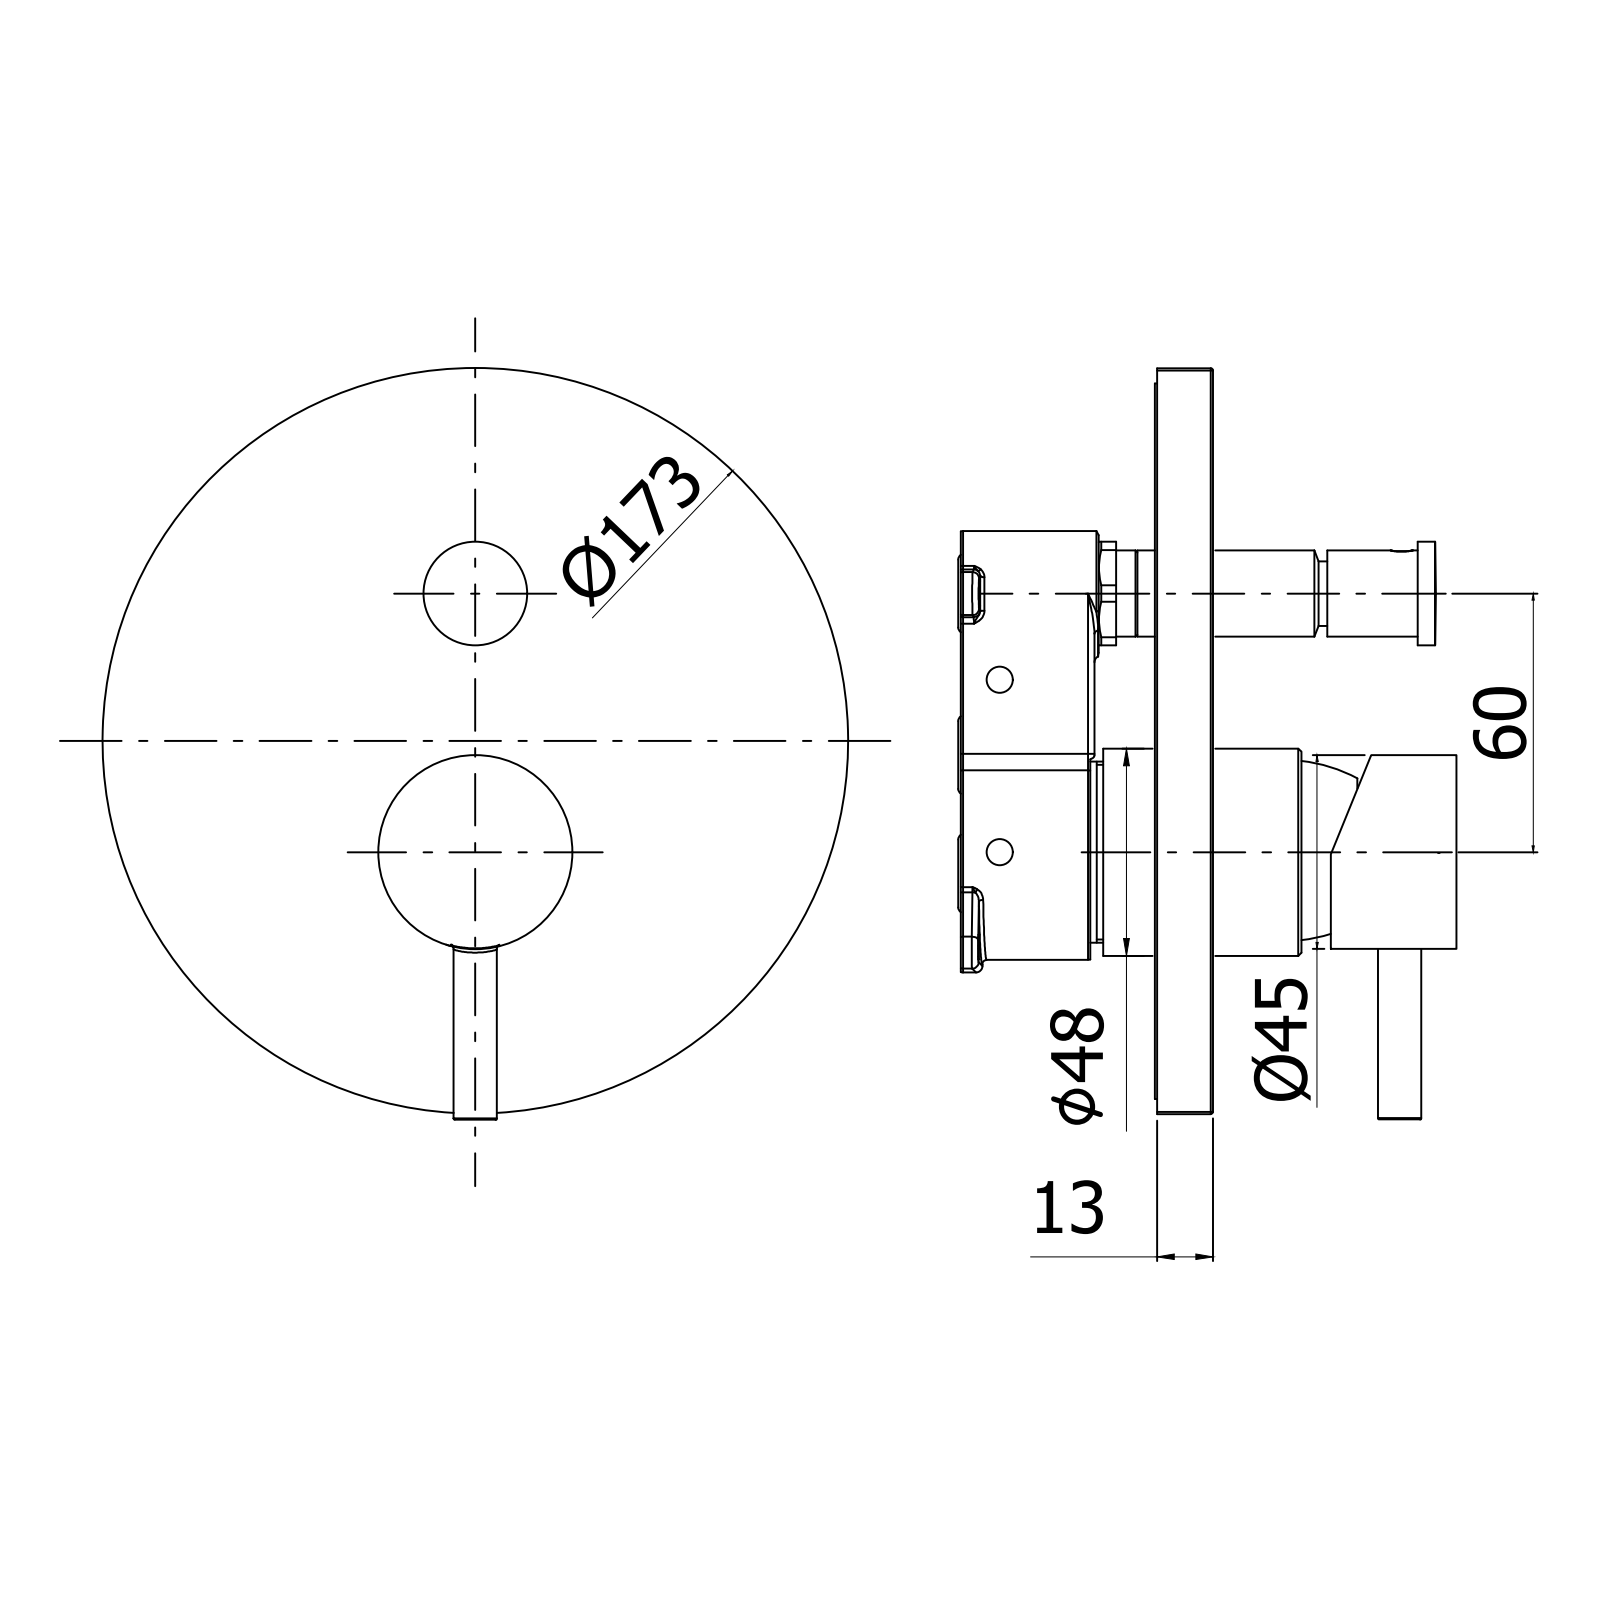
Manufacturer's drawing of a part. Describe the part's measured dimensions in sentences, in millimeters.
The part is named "LIGBOX015CR". Its 3-D file was written by "CREO PARAMETRIC BY PTC INC, 2020044 (CONFIG_CONTROL_DESIGN)". It is 1 solid with 169 faces: 34 planar, 48 cylindrical and 87 other. Overall it measures 174.25 by 173 by 58.69 millimeters. Its volume is 375 572 cubic millimeters and its surface area 71 572 square millimeters. Round holes: 1 of diameter 3, 1 of diameter 5.5. Round bosses or shafts: 1 of diameter 173, 1 of diameter 48.1, 1 of diameter 44.5, 1 of diameter 24, 1 of diameter 20, 1 of diameter 15, 1 of diameter 10, 1 of diameter 7.6. Partial cylindrical surfaces (rounded edges, fillets, slot ends): 8 of radius 0.5, 1 of radius 2.5. The main face-to-face distances are 13, 26.5, 54.3, 41.3, 14.8, 39.5, 13.5, 27.8, 53.3, 40.3.
